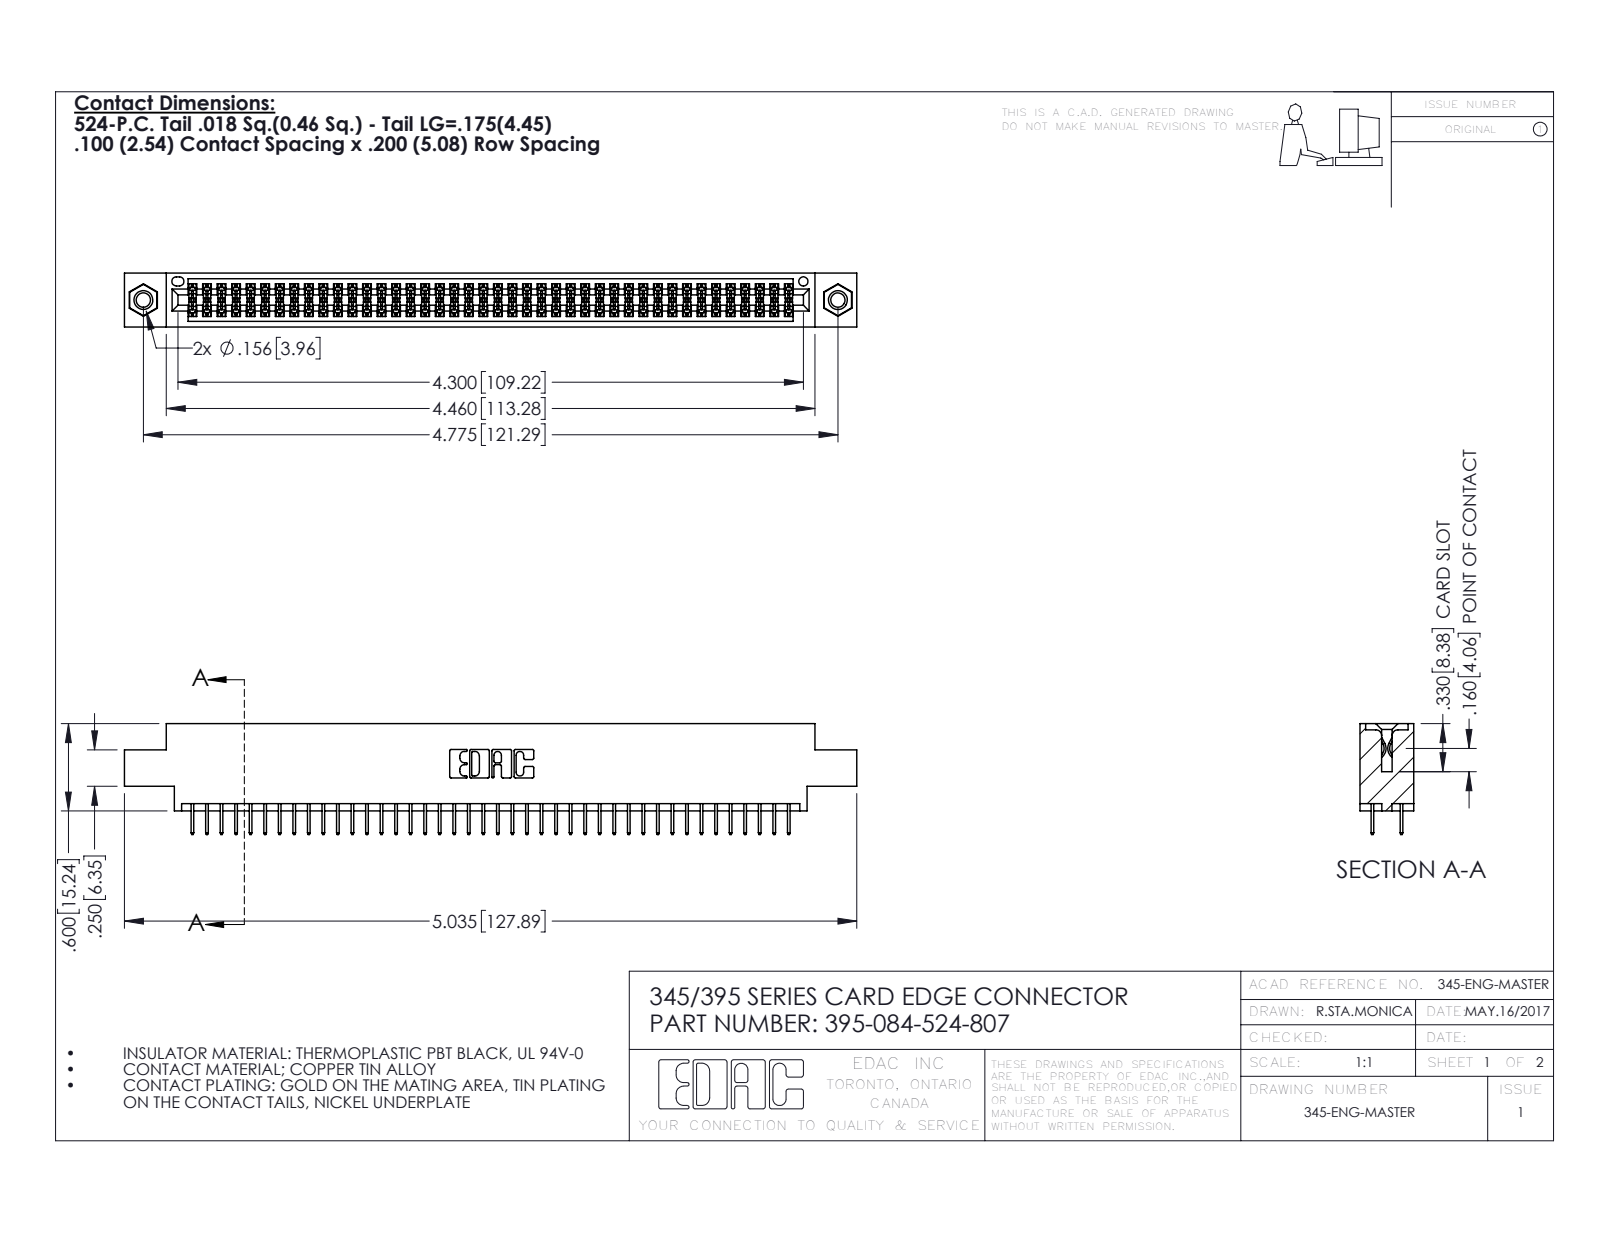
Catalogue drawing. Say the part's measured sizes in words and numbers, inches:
The part is named "395-084-524-807; 345-250-001_345-250-005-103; 345 Part_0.170 Offset - 0.156 Dia-TI; 345-292-001_345-293-124". Its 3-D file was written by "SolidWorks 2016 (CONFIG_CONTROL_DESIGN)". It is 87 solids with 4726 faces: 3392 planar, 1318 cylindrical and 16 other. Overall it measures 5.035 by 0.762 by 0.37 inches. Its volume is 0.743 cubic inches and its surface area 27.63 square inches. Round holes: 2 of diameter 0.098, 2 of diameter 0.125, 2 of diameter 0.156, 1 of diameter 0.064. Round bosses or shafts: 2 of diameter 0.155. Partial cylindrical surfaces (rounded edges, fillets, slot ends): 126 of radius 0.006, 22 of radius 0.01, 6 of radius 0.007, 6 of radius 0.031, 3 of radius 0.026, 2 of radius 0.014, 2 of radius 0.019, 2 of radius 0.022. The main face-to-face distances are 0.072, 0.298, 0.2, 0.37, 0.098, 0.272, 0.025, 0.225, 0.175, 0.072. The hole center spacings are 0.27, 4.539, 4.775.
